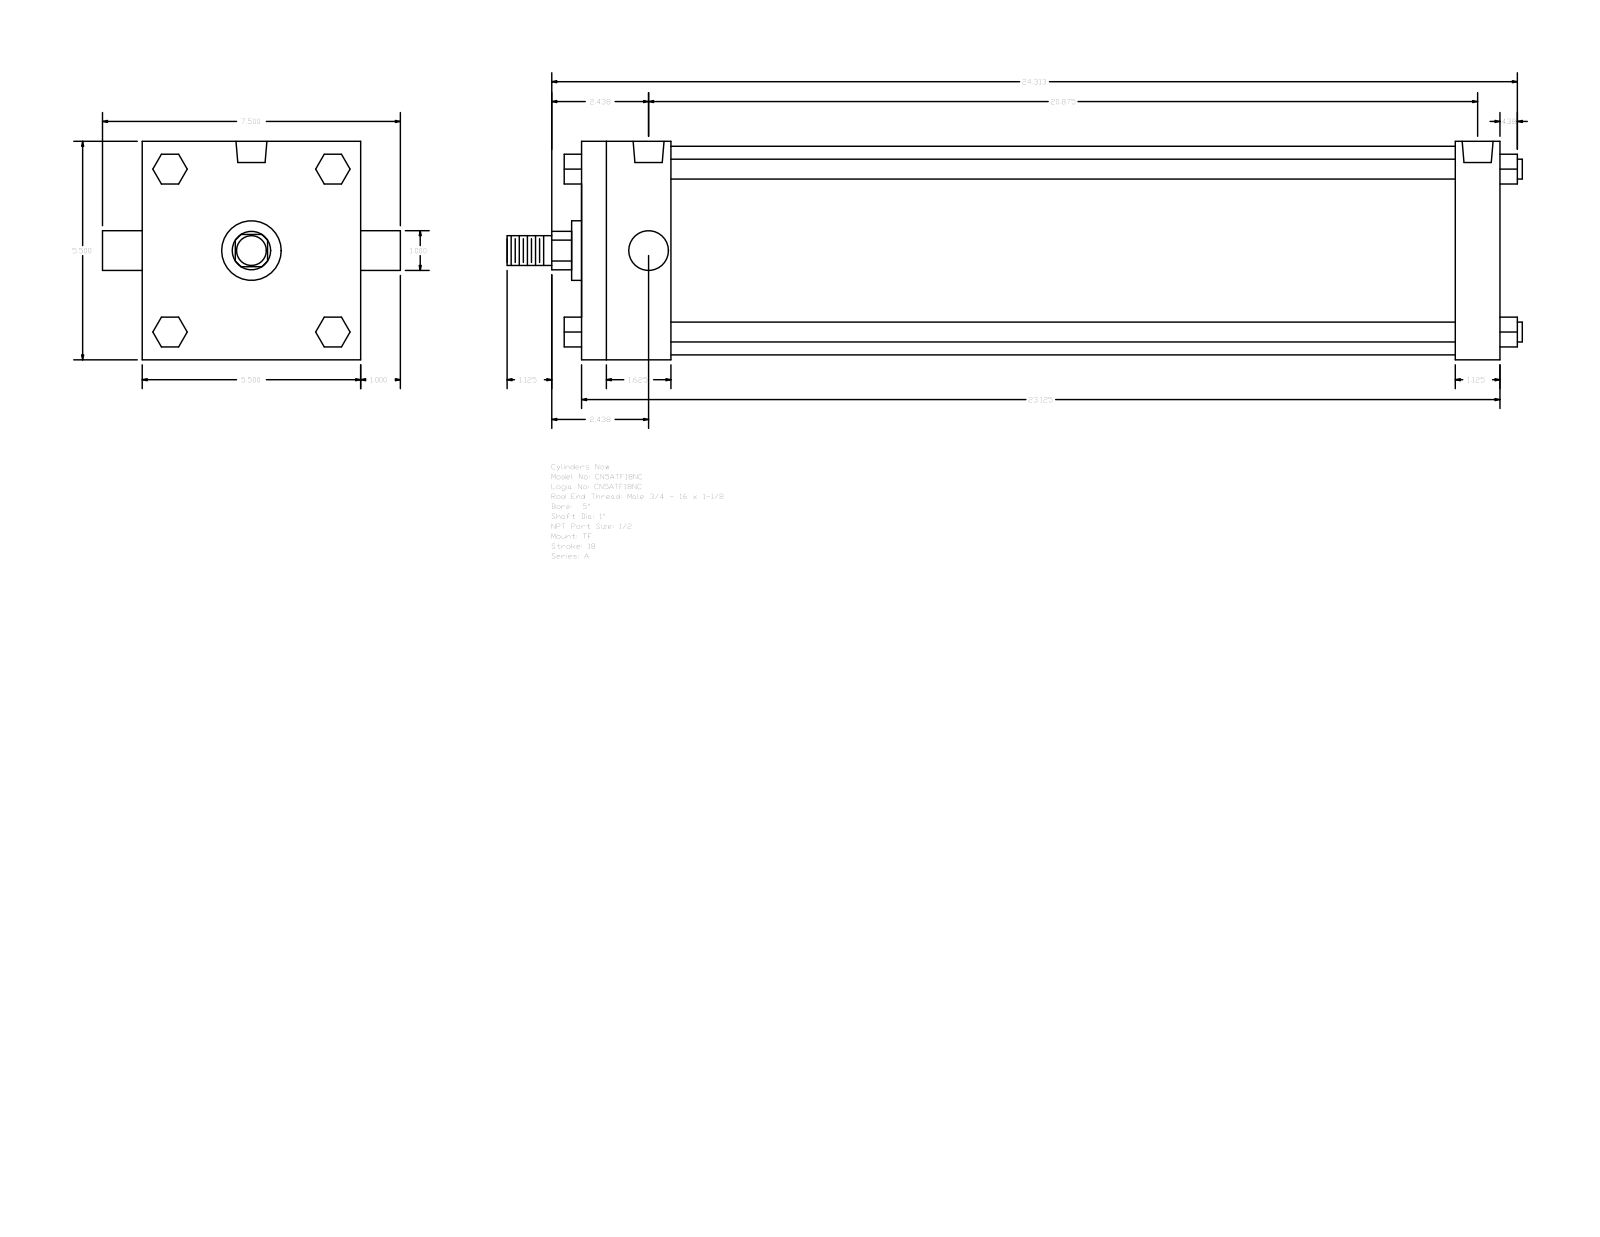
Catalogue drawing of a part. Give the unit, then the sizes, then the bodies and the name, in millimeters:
Units: millimetres
Overall size (bounding box): 649.29 × 190.5 × 139.7
Round holes (diameter × count): ⌀8.73 ×3, ⌀19.77 ×2
Round bosses / shafts (diameter × count): ⌀12.7 ×4, ⌀25.4 ×2, ⌀133.35 ×1, ⌀38.1 ×1, ⌀19.05 ×1
Partial cylindrical surfaces — rounded edges, fillets, slot ends (radius × count): R12.29 ×1
Main face-to-face distances: 139.7, 587.37, 28.57, 558.8, 57.15, 501.65, 530.22, 19.05, 52.07, 90.18
Hole centre spacings: 2.39, 527.84, 525.45, 530.23
Bodies: 0 solids, 120 faces (92 planar, 28 cylindrical, 0 other)
Part name (STEP PRODUCT): A_TF__0500_1
STEP written by: GSSL Pune (CONFIG_CONTROL_DESIGN)
